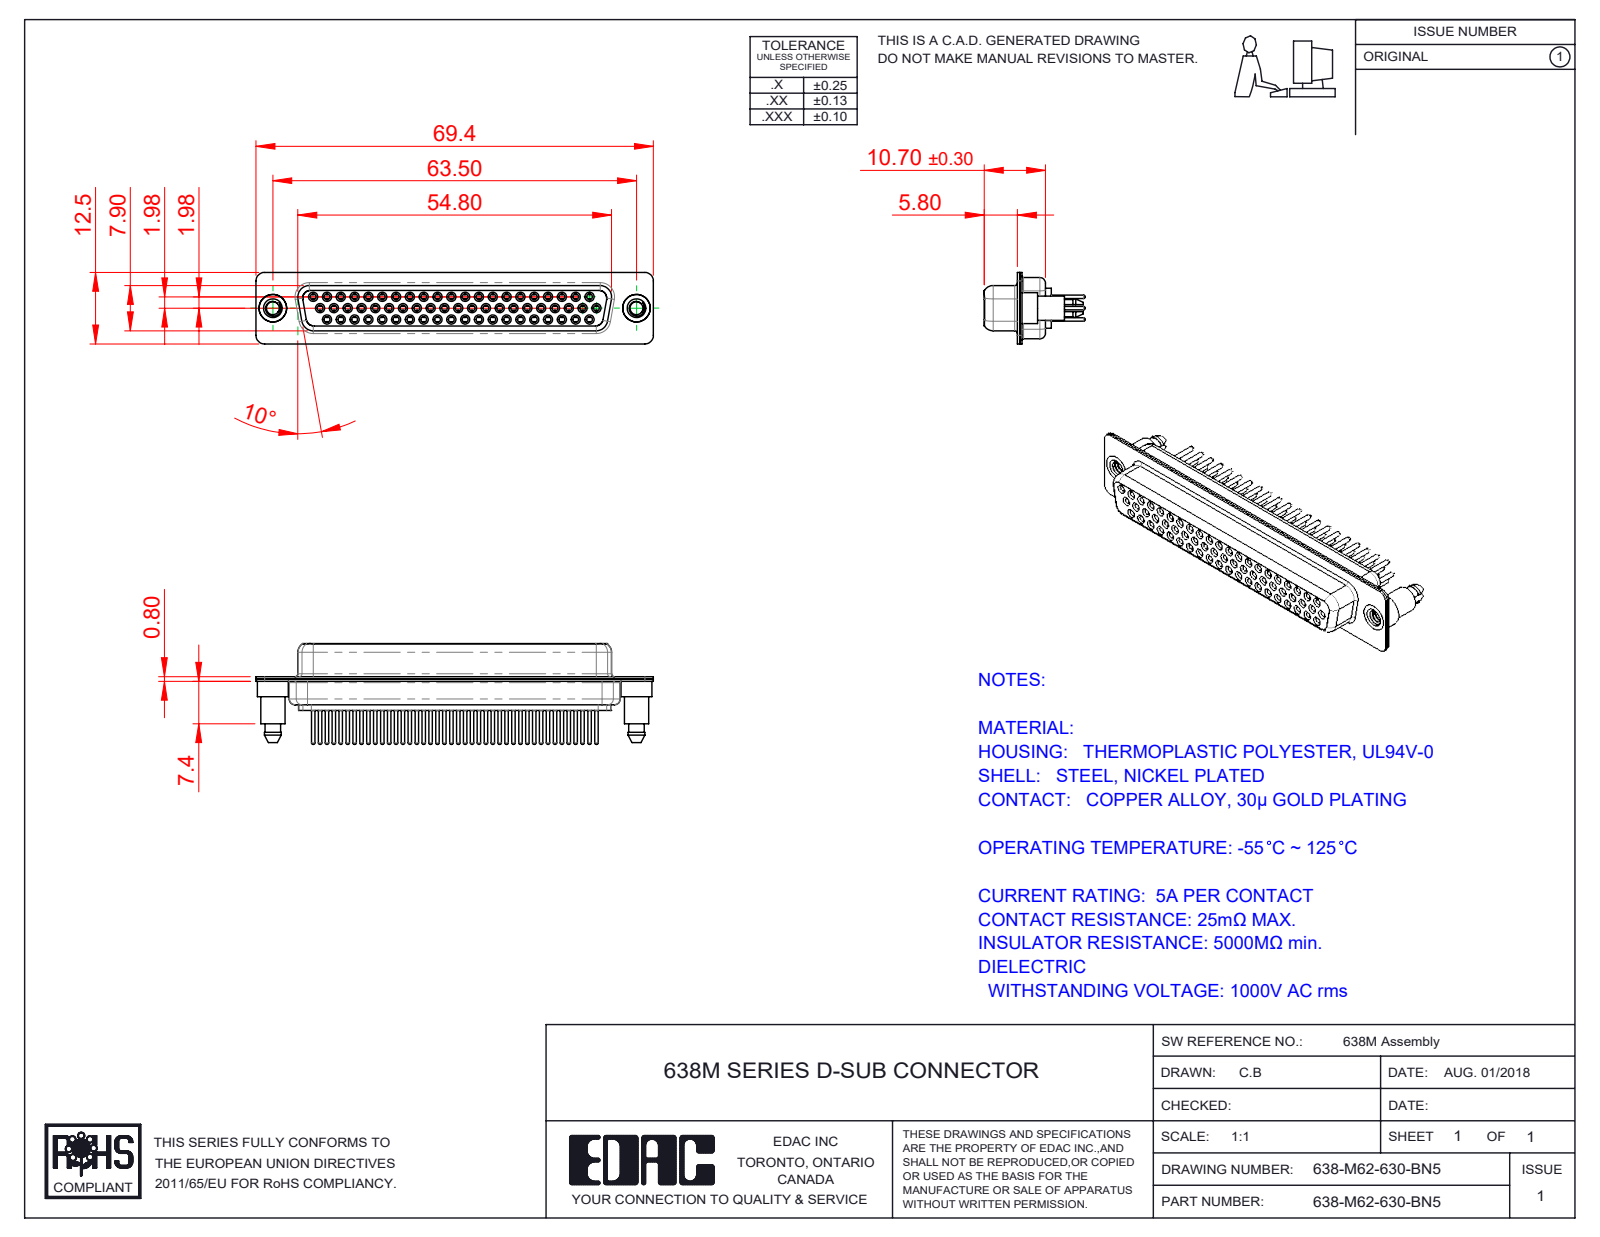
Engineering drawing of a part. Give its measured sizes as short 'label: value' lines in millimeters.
name: 638M Contact Row 1_30; 638M Contact Row 2_30; 638M 4-40 Threaded Boardlock; 638M Shell Front_62 Contacts (+4 more)
written by: SolidWorks 2020 (CONFIG_CONTROL_DESIGN)
unit: mm
bodies: 67 solids, 3739 faces (1013 planar, 1347 cylindrical, 1379 other)
size: 69.4 × 17.6 × 12.5
volume: 5 116 mm³; area: 16 773 mm²
holes: 62× ⌀1, 62× ⌀1.1, 62× ⌀1.7, 62× ⌀1.8, 62× ⌀2, 2× ⌀2.26, 2× ⌀4, 2× ⌀4.8
bosses: 62× ⌀2.2, 62× ⌀1.6, 62× ⌀1.5, 62× ⌀0.6, 2× ⌀5.4, 2× ⌀4.9, 2× ⌀4.25
rounds: 18× R1.5, 12× R2, 10× R1.6, 8× R1.35, 4× R0.25, 4× R0.5, 4× R0.6, 4× R0.65
face distances: 0.4, 1.4, 0.45, 8.45, 8.9, 1, 1.8, 6.2, 7.05, 1.85
hole spacings: 7.24, 2.32, 2.41, 4.13, 9.65, 4.83, 14.48, 16.89
